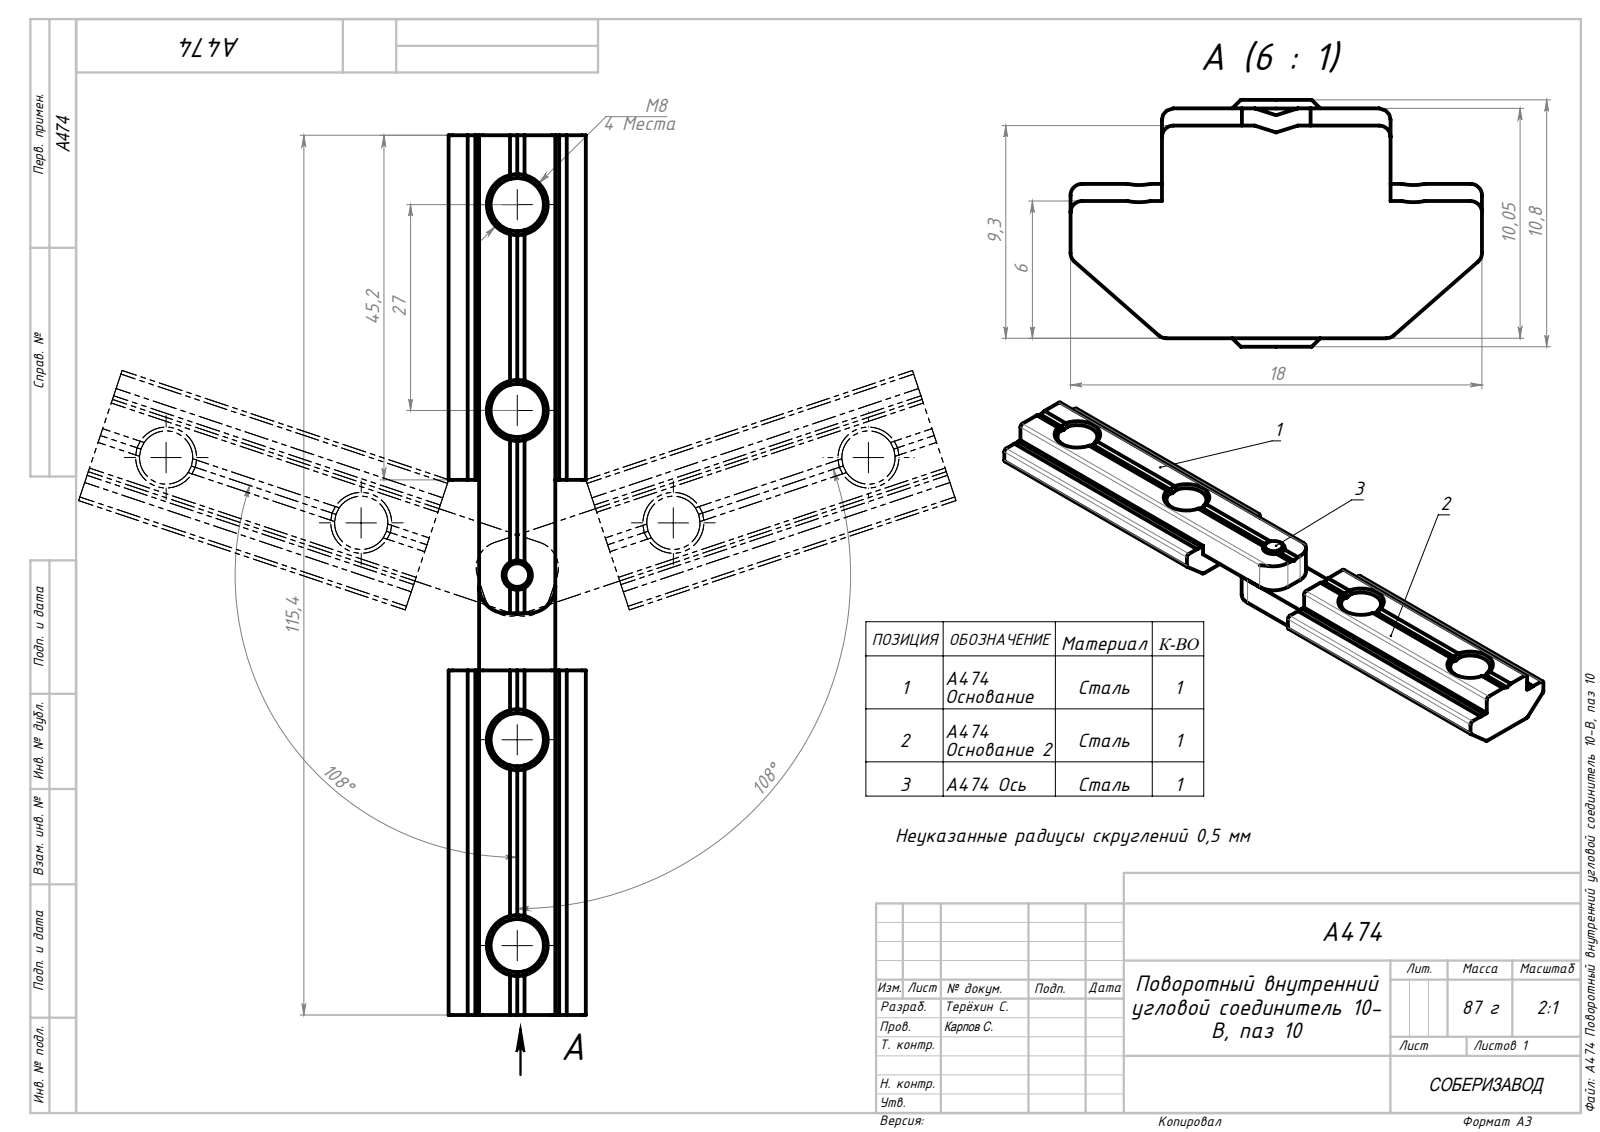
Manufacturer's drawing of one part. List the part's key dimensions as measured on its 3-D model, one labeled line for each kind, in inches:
Part name (STEP PRODUCT): A474 Основание 2_00; A474 Ось_00; A474 Основание_00; A474 Поворотный внутренний угловой соединитель 10-В, паз 10
STEP written by: SolidWorks 2021 (AUTOMOTIVE_DESIGN)
Units: inches
Bodies: 3 solids, 137 faces (54 planar, 38 cylindrical, 45 other)
Overall size (bounding box): 4.543 × 0.709 × 0.425
Volume: 0.713 in³ · Surface area: 10.25 in²
Round holes (diameter × count): ⌀0.276 ×4, ⌀0.118 ×1
Partial cylindrical surfaces — rounded edges, fillets, slot ends (radius × count): R0.02 ×16, R0.099 ×4, R0.138 ×4
Main face-to-face distances: 0.03, 0.366, 0.236, 0.13, 0.022, 0.394, 0.396, 0.193, 0.163, 0.203
Hole centre spacings: 0.85, 1.063, 1.913, 2.764, 1.701, 3.827
